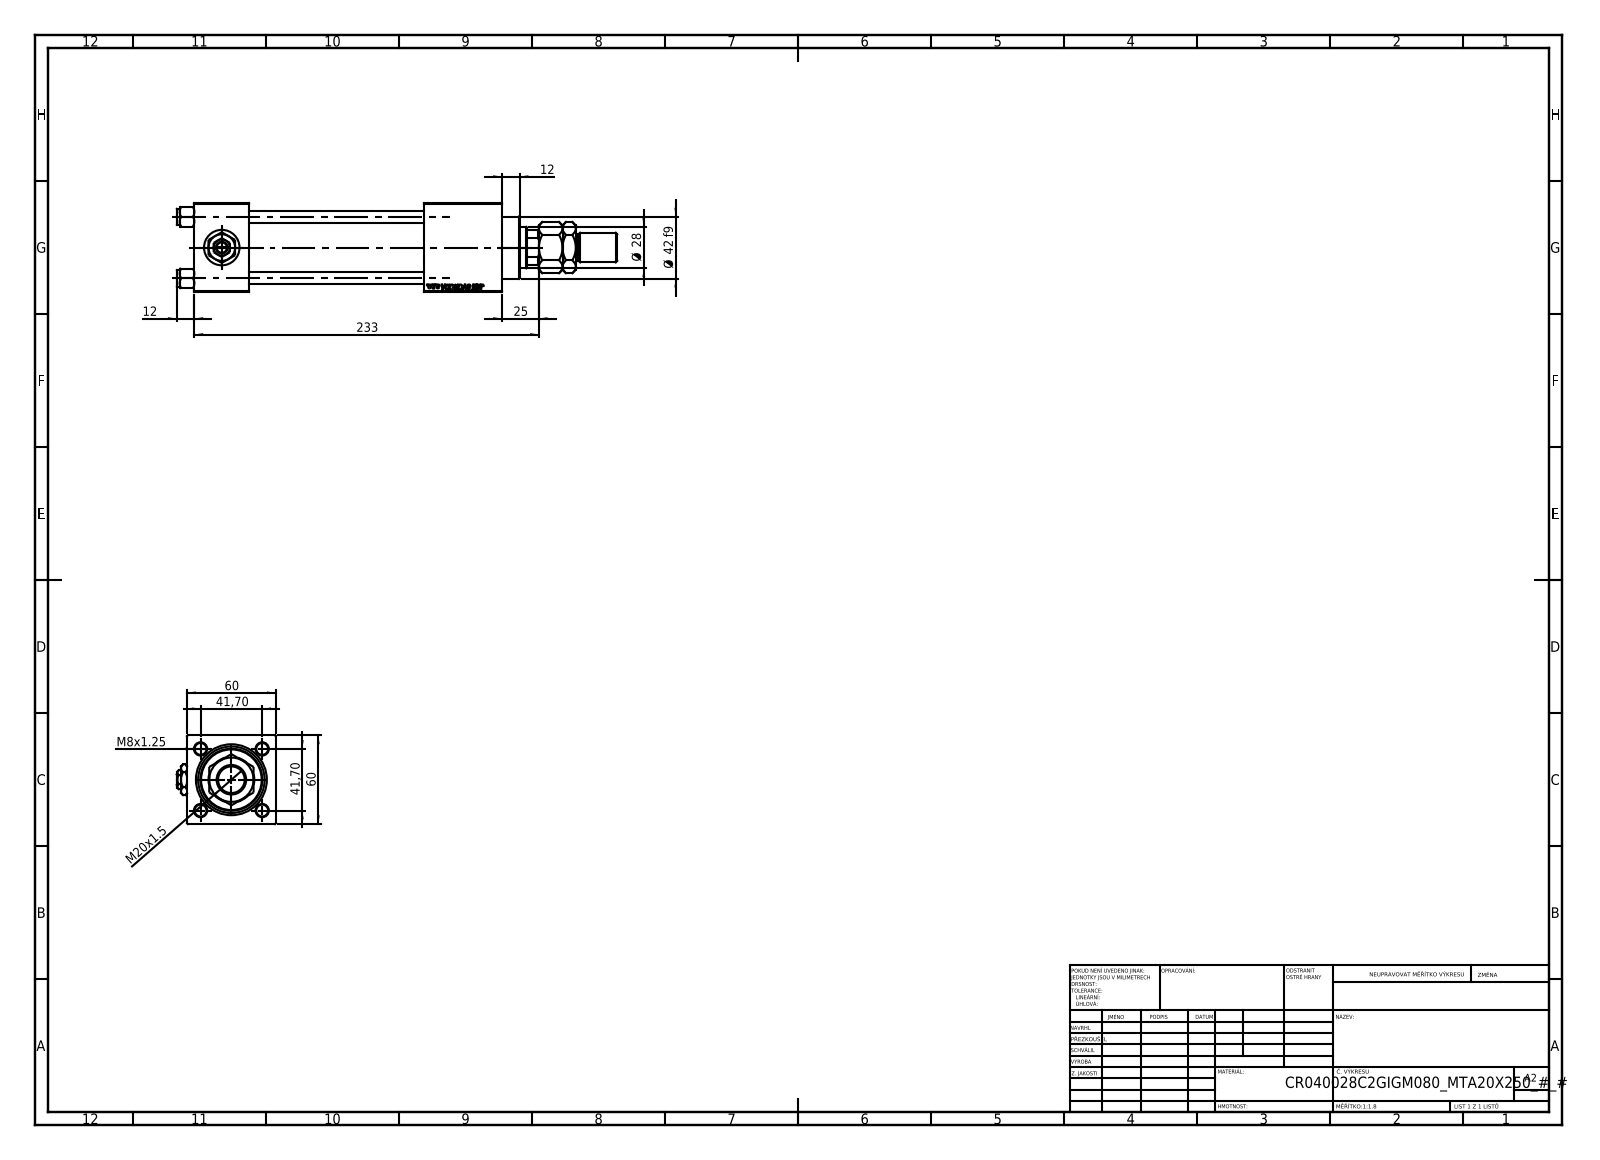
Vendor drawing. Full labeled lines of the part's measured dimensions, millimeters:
Part name (STEP PRODUCT): MTA; Zatka_pro_OIL_PORT; V215CR_C_TYCINKA; V215CR_C_Body (+3 more)
STEP written by: SolidWorks 2019 (CONFIG_CONTROL_DESIGN)
Units: millimetres
Bodies: 13 solids, 1251 faces (565 planar, 98 cylindrical, 588 other)
Overall size (bounding box): 298 × 67 × 60
Volume: 524 063 mm³ · Surface area: 146 462 mm²
Round holes (diameter × count): ⌀8 ×4, ⌀7 ×2, ⌀16.66 ×2, ⌀24 ×2, ⌀18.5 ×1, ⌀28 ×1, ⌀31 ×1, ⌀40 ×1, ⌀45 ×1
Round bosses / shafts (diameter × count): ⌀11 ×4, ⌀46 ×1, ⌀42 ×1, ⌀20 ×1, ⌀18 ×1
Partial cylindrical surfaces — rounded edges, fillets, slot ends (radius × count): R13.5 ×1
Main face-to-face distances: 60, 37, 155, 118, 53, 179.3, 142.3, 24.3, 208, 171
Hole centre spacings: 29.49, 41.7, 58.97
